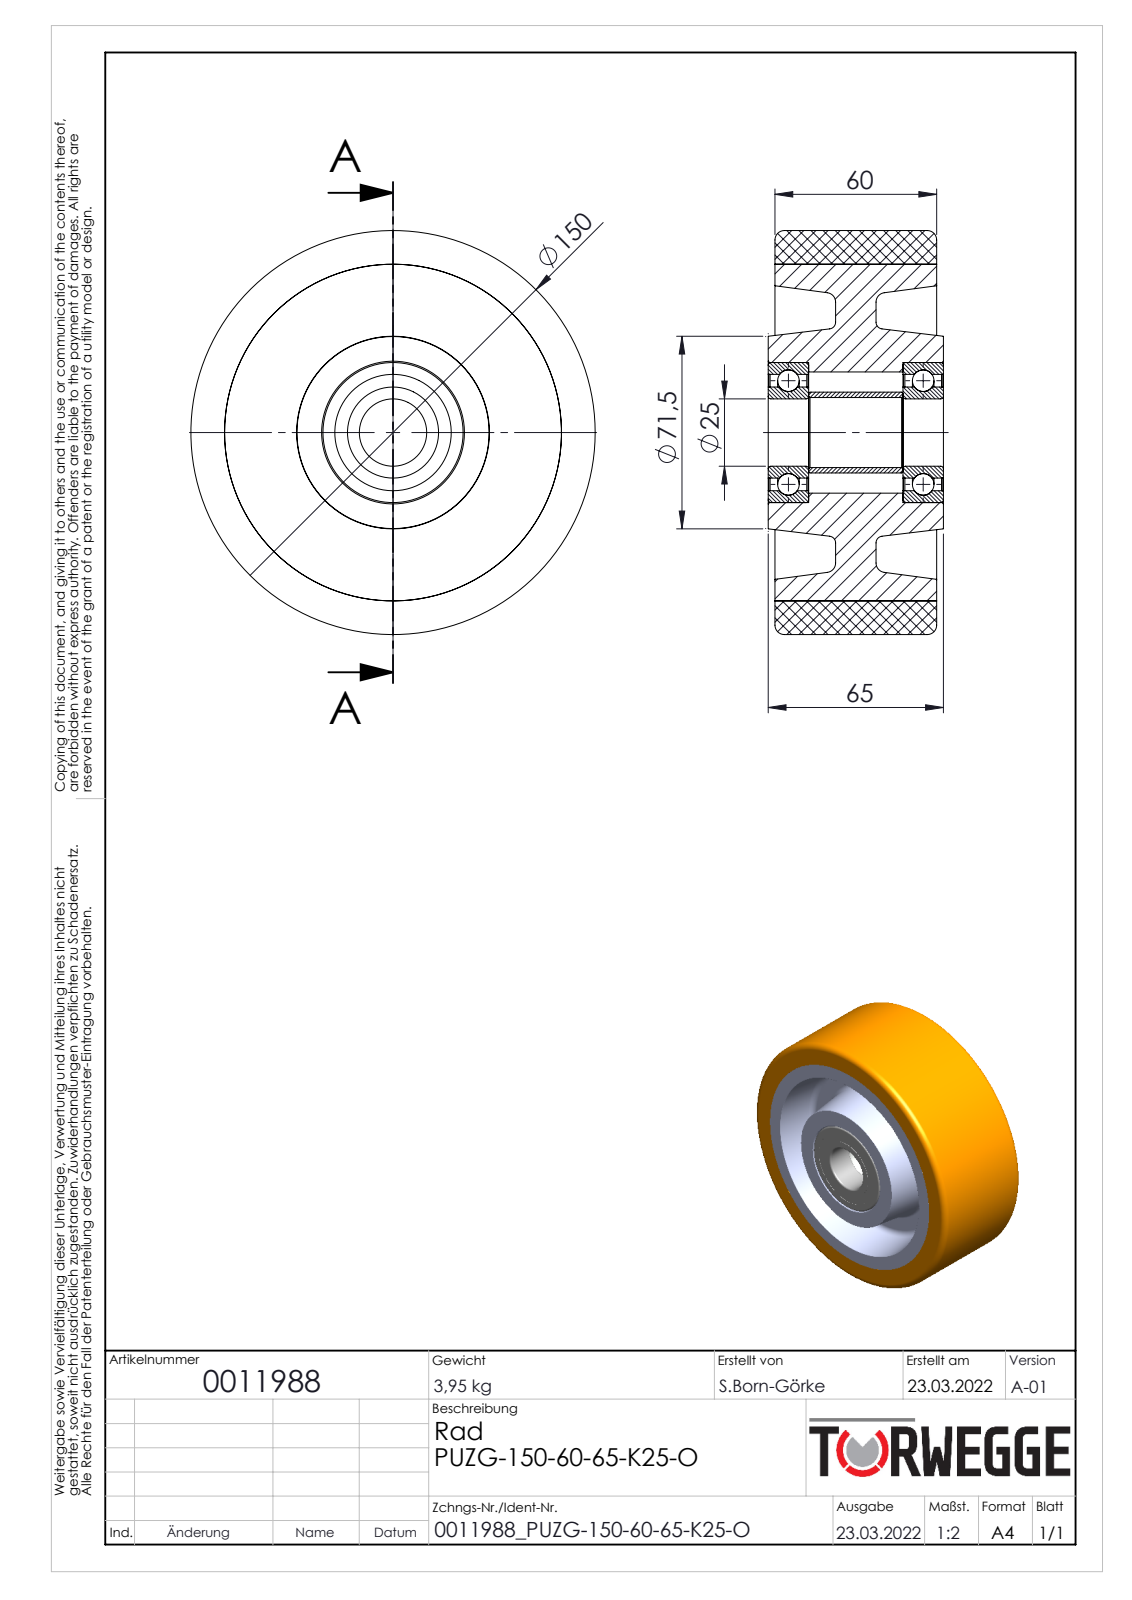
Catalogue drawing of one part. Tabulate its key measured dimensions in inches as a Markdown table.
| quantity | value |
| --- | --- |
| part name | 0011988 |
| STEP written by | SolidWorks 2020 (AUTOMOTIVE_DESIGN) |
| units | inches |
| bodies | 13 solids, 160 faces (28 planar, 56 cylindrical, 76 other) |
| overall size | 5.906 × 5.906 × 2.559 |
| volume | 49.33 in³ |
| surface area | 270.7 in² |
| round holes (diameter × count) | 0.984 × 1, 1.024 × 1, 1.331 × 1, 1.701 × 1, 1.772 × 1, 2.047 × 1, 4.921 × 1 |
| round bosses / shafts (diameter × count) | 5.906 × 1, 1.181 × 1 |
| main face-to-face distances | 0.984, 2.362, 0.098, 2.461, 1.969, 0.591, 1.575, 0.886, 1.476, 0.492 |
